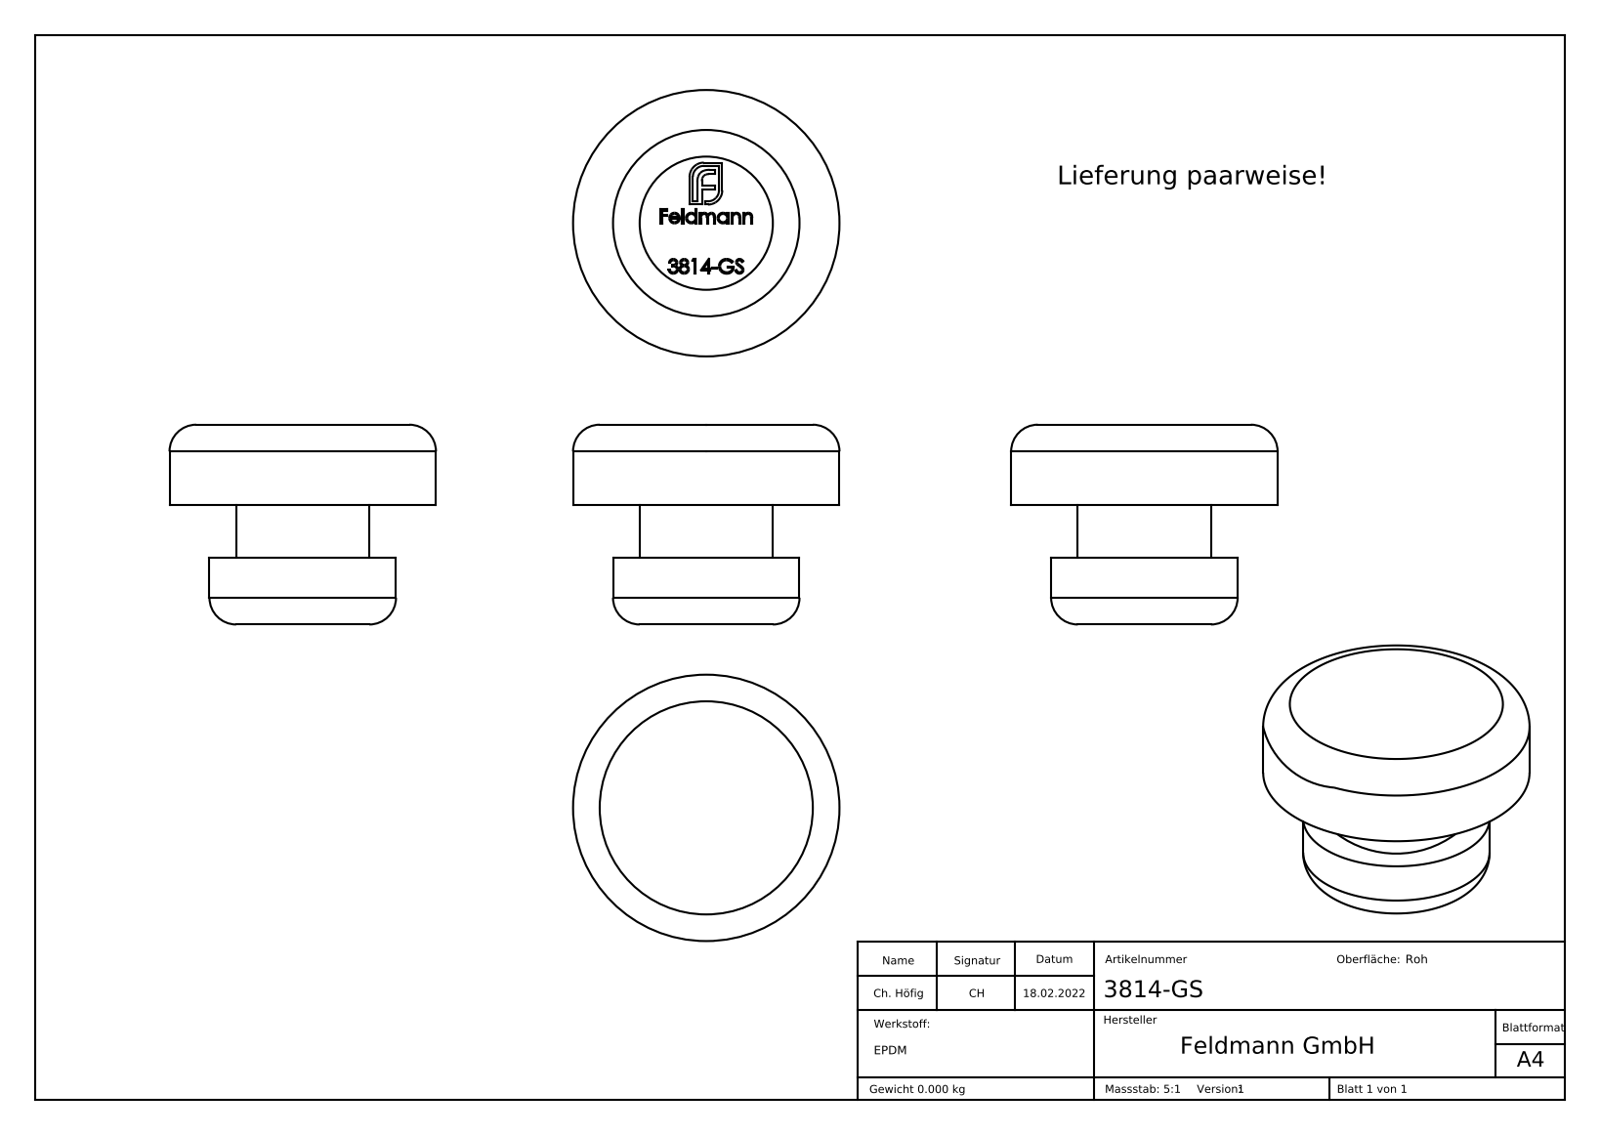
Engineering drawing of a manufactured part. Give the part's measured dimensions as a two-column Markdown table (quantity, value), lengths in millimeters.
| quantity | value |
| --- | --- |
| part name | 3814-GS |
| STEP written by | SolidWorks 2018 (CONFIG_CONTROL_DESIGN) |
| units | millimeters |
| bodies | 1 solid, 267 faces (134 planar, 6 cylindrical, 127 other) |
| overall size | 10 × 10 × 7.5 |
| volume | 360 mm³ |
| surface area | 356 mm² |
| round bosses / shafts (diameter × count) | 10 × 1, 7 × 1, 5 × 1 |
| main face-to-face distances | 3, 2, 5, 2.5, 4.5, 7.5, 2.4, 4.4, 7.4, 0.47 |
